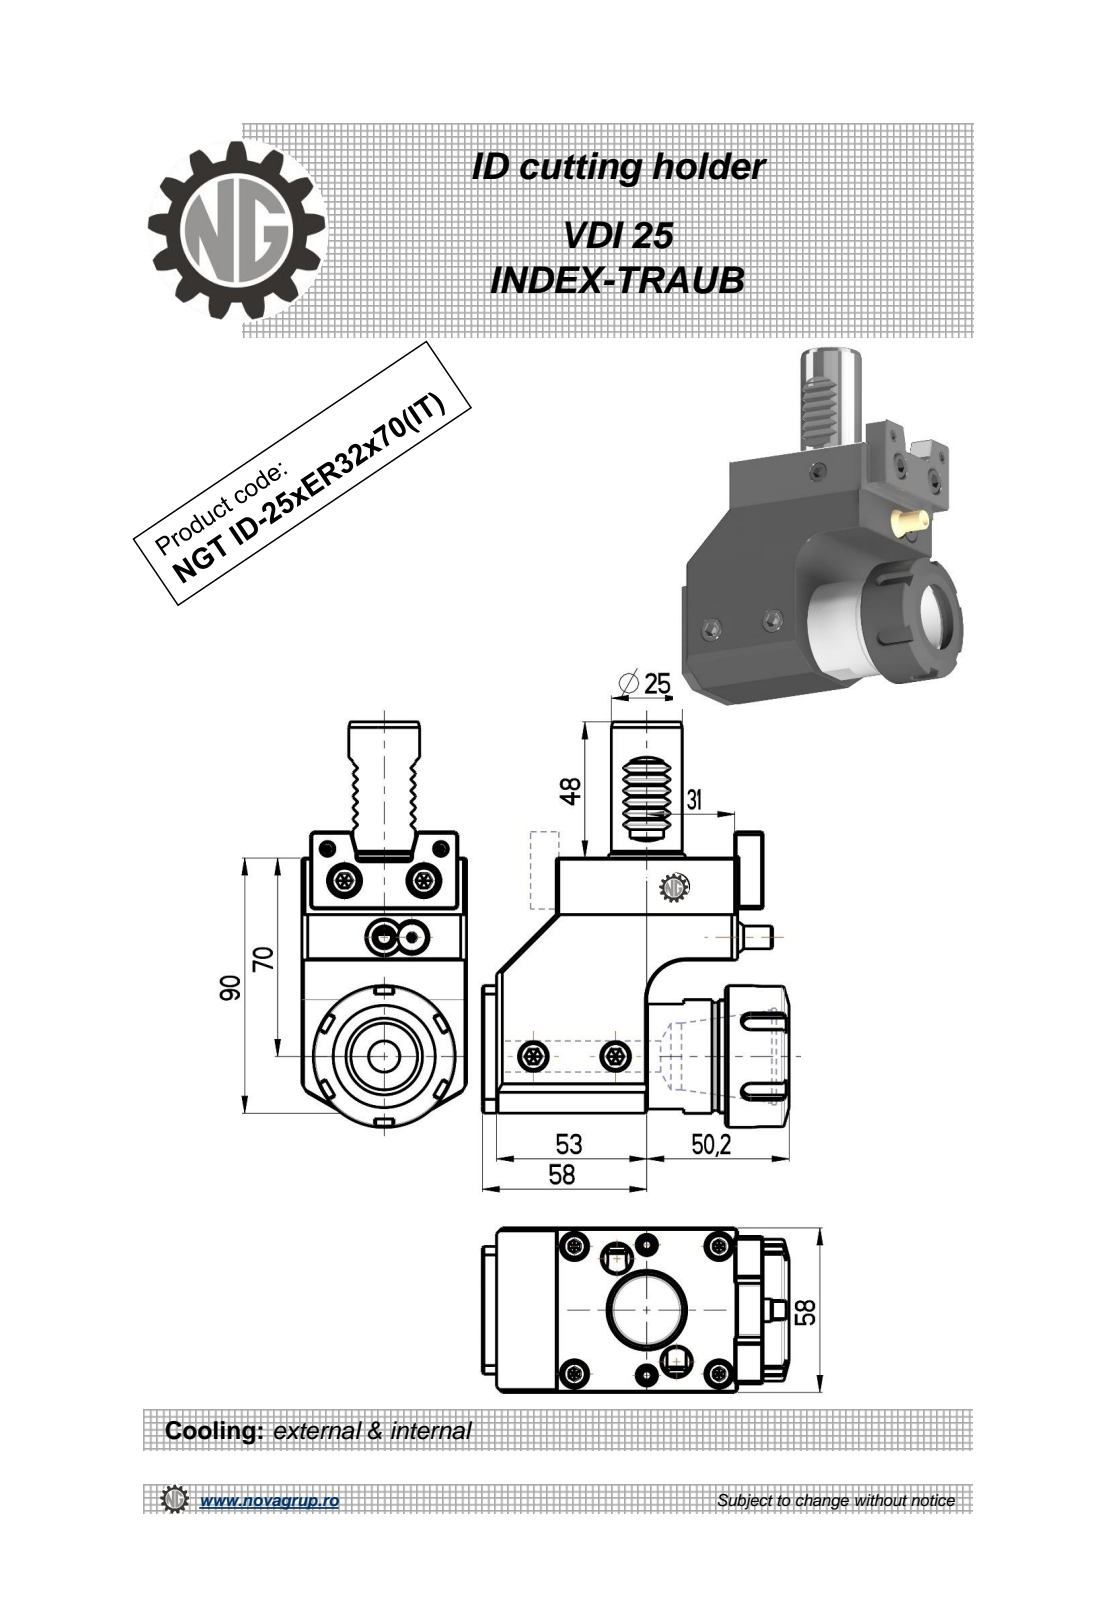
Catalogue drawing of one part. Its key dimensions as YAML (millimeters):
part_name: "NGT_ID_25_ER32_70_IT"
step_written_by: "PRO/ENGINEER BY PARAMETRIC TECHNOLOGY CORPORATION, 2010280 (CONFIG_CONTROL_DESIGN)"
units: millimeters
bodies: {solids: 1, faces: 582, planar: 288, cylindrical: 138, other: 156}
overall_size: [143, 108.2, 58]
volume: 382003
surface_area: 57933
round_holes:
  - {diameter: 5, count: 3}
  - {diameter: 4.2, count: 2}
  - {diameter: 8.5, count: 2}
  - {diameter: 10, count: 2}
  - {diameter: 11, count: 1}
  - {diameter: 23.5, count: 1}
  - {diameter: 27, count: 1}
  - {diameter: 32.8, count: 1}
  - {diameter: 41, count: 1}
round_bosses_or_shafts:
  - {diameter: 10, count: 4}
  - {diameter: 25, count: 2}
  - {diameter: 50, count: 1}
  - {diameter: 40.1, count: 1}
  - {diameter: 40, count: 1}
  - {diameter: 38, count: 1}
  - {diameter: 8, count: 1}
partial_cylinders:
  - {radius: 0.2, count: 20}
  - {radius: 0.3, count: 12}
  - {radius: 0.26, count: 10}
  - {radius: 0.51, count: 10}
  - {radius: 3, count: 5}
  - {radius: 1, count: 2}
  - {radius: 8, count: 2}
  - {radius: 14, count: 1}
face_to_face_distances: [58, 90, 32, 18, 5, 26, 99, 9, 94, 73]
hole_center_spacings: [12.71, 24.41, 35.8, 37.06, 63.56, 75.88, 1.5, 28]
